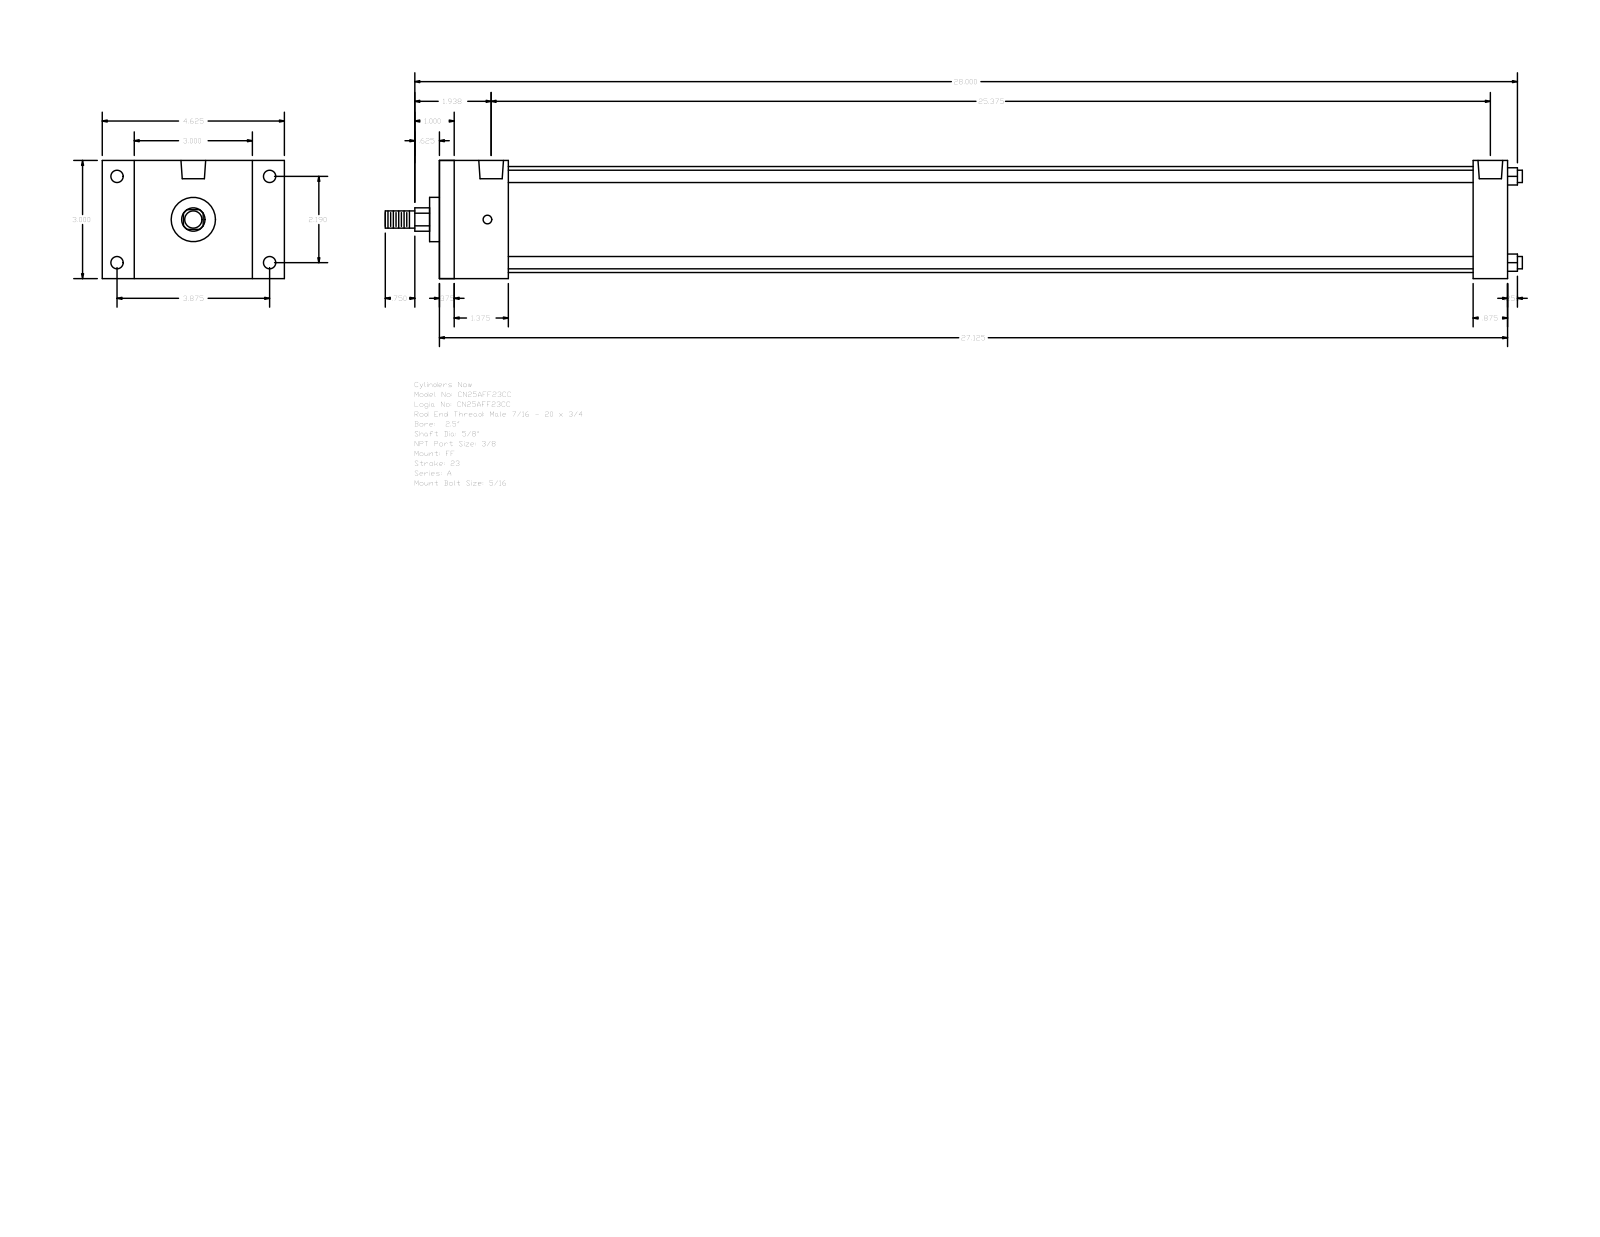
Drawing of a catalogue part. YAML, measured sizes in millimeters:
part_name: "A_FF__0250_0.625"
step_written_by: "GSSL Pune (CONFIG_CONTROL_DESIGN)"
units: millimeters
bodies: {solids: 0, faces: 92, planar: 64, cylindrical: 28, other: 0}
overall_size: [733.42, 117.47, 76.2]
round_holes:
  - {diameter: 5.56, count: 4}
  - {diameter: 7.94, count: 4}
  - {diameter: 15.93, count: 2}
round_bosses_or_shafts:
  - {diameter: 7.94, count: 4}
  - {diameter: 68.33, count: 1}
  - {diameter: 28.57, count: 1}
  - {diameter: 15.88, count: 1}
  - {diameter: 11.11, count: 1}
partial_cylinders:
  - {radius: 7.54, count: 1}
face_to_face_distances: [76.2, 688.97, 9.52, 679.45, 44.45, 34.93, 666.74, 657.22, 622.29, 644.52]
hole_center_spacings: [2.38, 55.62, 98.42, 113.05, 646.91, 649.29, 644.53]
